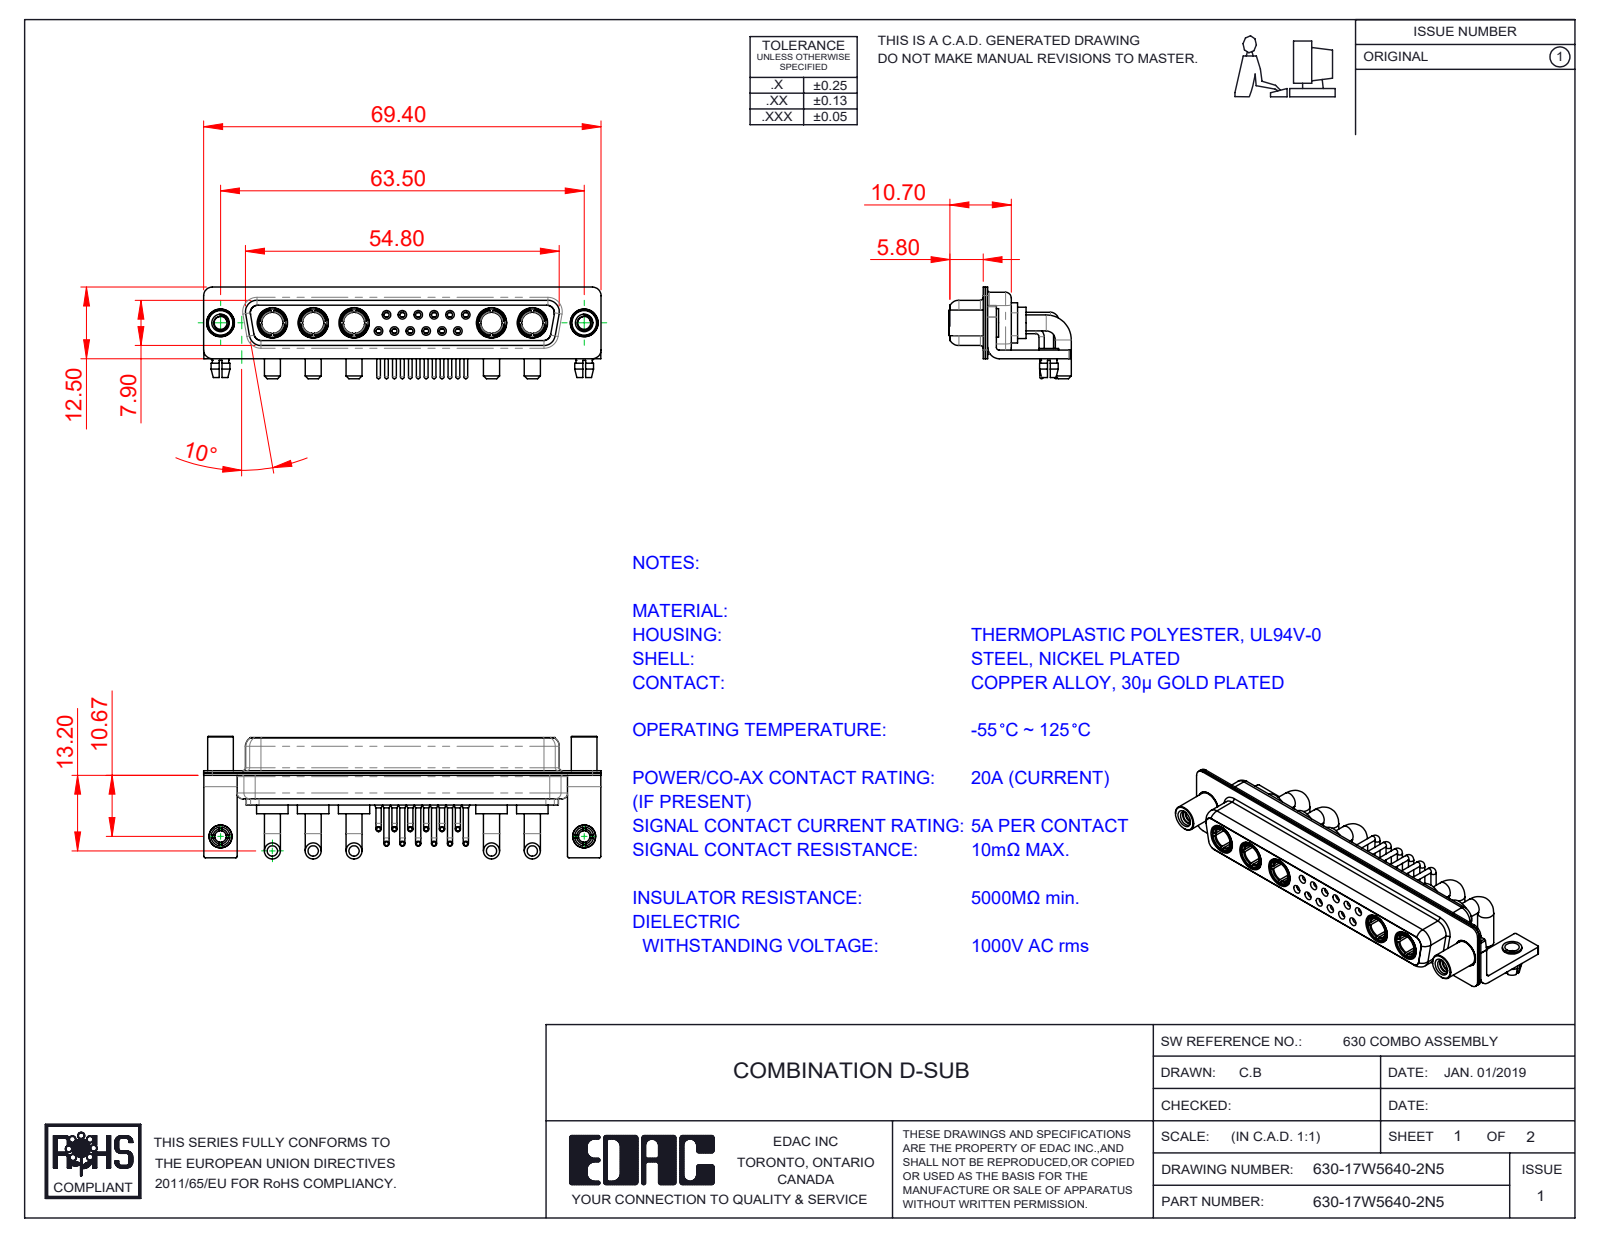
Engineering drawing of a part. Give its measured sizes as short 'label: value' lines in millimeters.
name: Power Socket_20A RA; 630Combo Shell Rear_37 Contacts; 630Combo Housing_17W5; 630Combo Board Lock (+6 more)
written by: SolidWorks 2020 (CONFIG_CONTROL_DESIGN)
unit: mm
bodies: 31 solids, 1485 faces (462 planar, 630 cylindrical, 393 other)
size: 69.4 × 21.4 × 16
volume: 6 107 mm³; area: 13 509 mm²
holes: 14× ⌀2, 12× ⌀0.9, 12× ⌀1.1, 12× ⌀1.5, 7× ⌀4.85, 6× ⌀1.6, 6× ⌀1.7, 5× ⌀3.7, 5× ⌀5.3, 2× ⌀2.26, 2× ⌀2.5, 2× ⌀3.2
bosses: 13× ⌀0.9, 12× ⌀0.65, 10× ⌀2.8, 7× ⌀1.6, 5× ⌀5.5, 5× ⌀5.2, 5× ⌀4.96, 5× ⌀4.75
rounds: 16× R0.25, 16× R1.5, 13× R2, 8× R1.35, 8× R1.6, 5× R0.5, 5× R2.1, 4× R0.6
face distances: 0.4, 0.45, 1.4, 8.45, 1.8, 8.9, 6.2, 7.05, 0.8, 7.5
hole spacings: 3.16, 2.77, 5.04, 5.54, 5.03, 7.49, 8.31, 10.11
